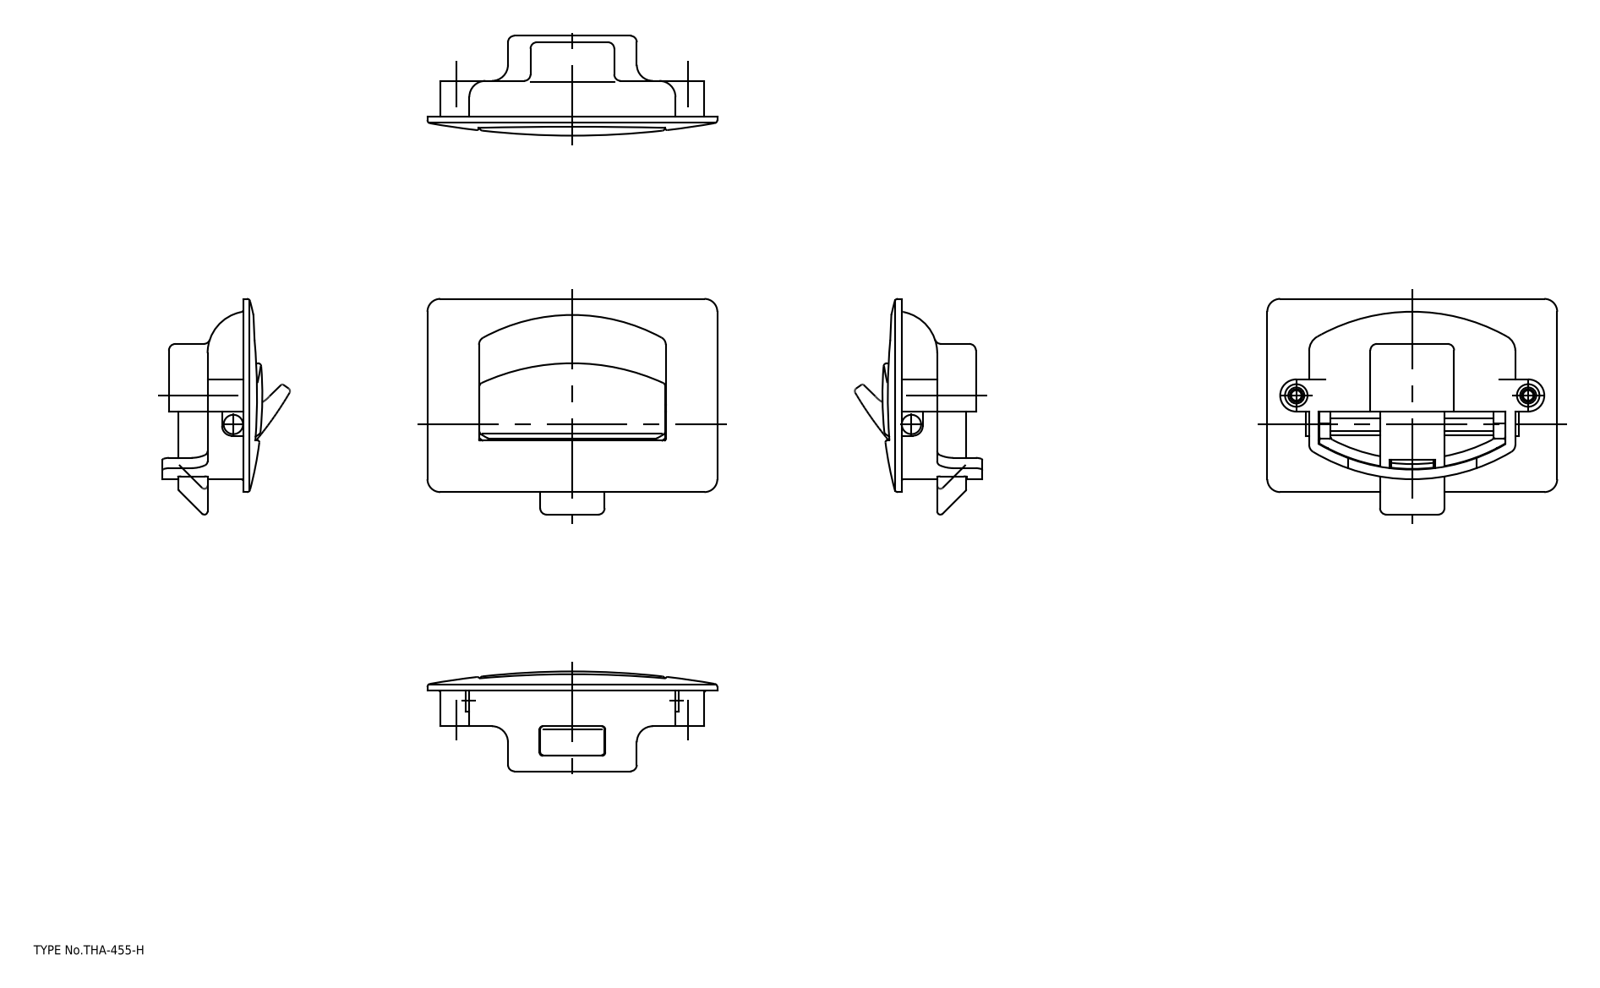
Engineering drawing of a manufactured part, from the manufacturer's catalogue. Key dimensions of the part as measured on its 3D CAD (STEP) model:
Part name (STEP PRODUCT): latch; handle; base
STEP written by: spGate 17.5.1 (AUTOMOTIVE_DESIGN)
Units: millimetres
Bodies: 3 solids, 222 faces (93 planar, 68 cylindrical, 61 other)
Overall size (bounding box): 90 × 67 × 31
Volume: 37 772 mm³ · Surface area: 26 829 mm²
Round holes (diameter × count): ⌀4 ×2
Round bosses / shafts (diameter × count): ⌀4 ×1
Partial cylindrical surfaces — rounded edges, fillets, slot ends (radius × count): R2 ×15, R1 ×10, R2.5 ×6, R4 ×4, R5 ×4, R0.5 ×3, R3 ×1, R8 ×1
Main face-to-face distances: 3, 11, 12, 23, 2.11, 13.11, 8, 2.5, 20, 39
Hole centre spacings: 72
